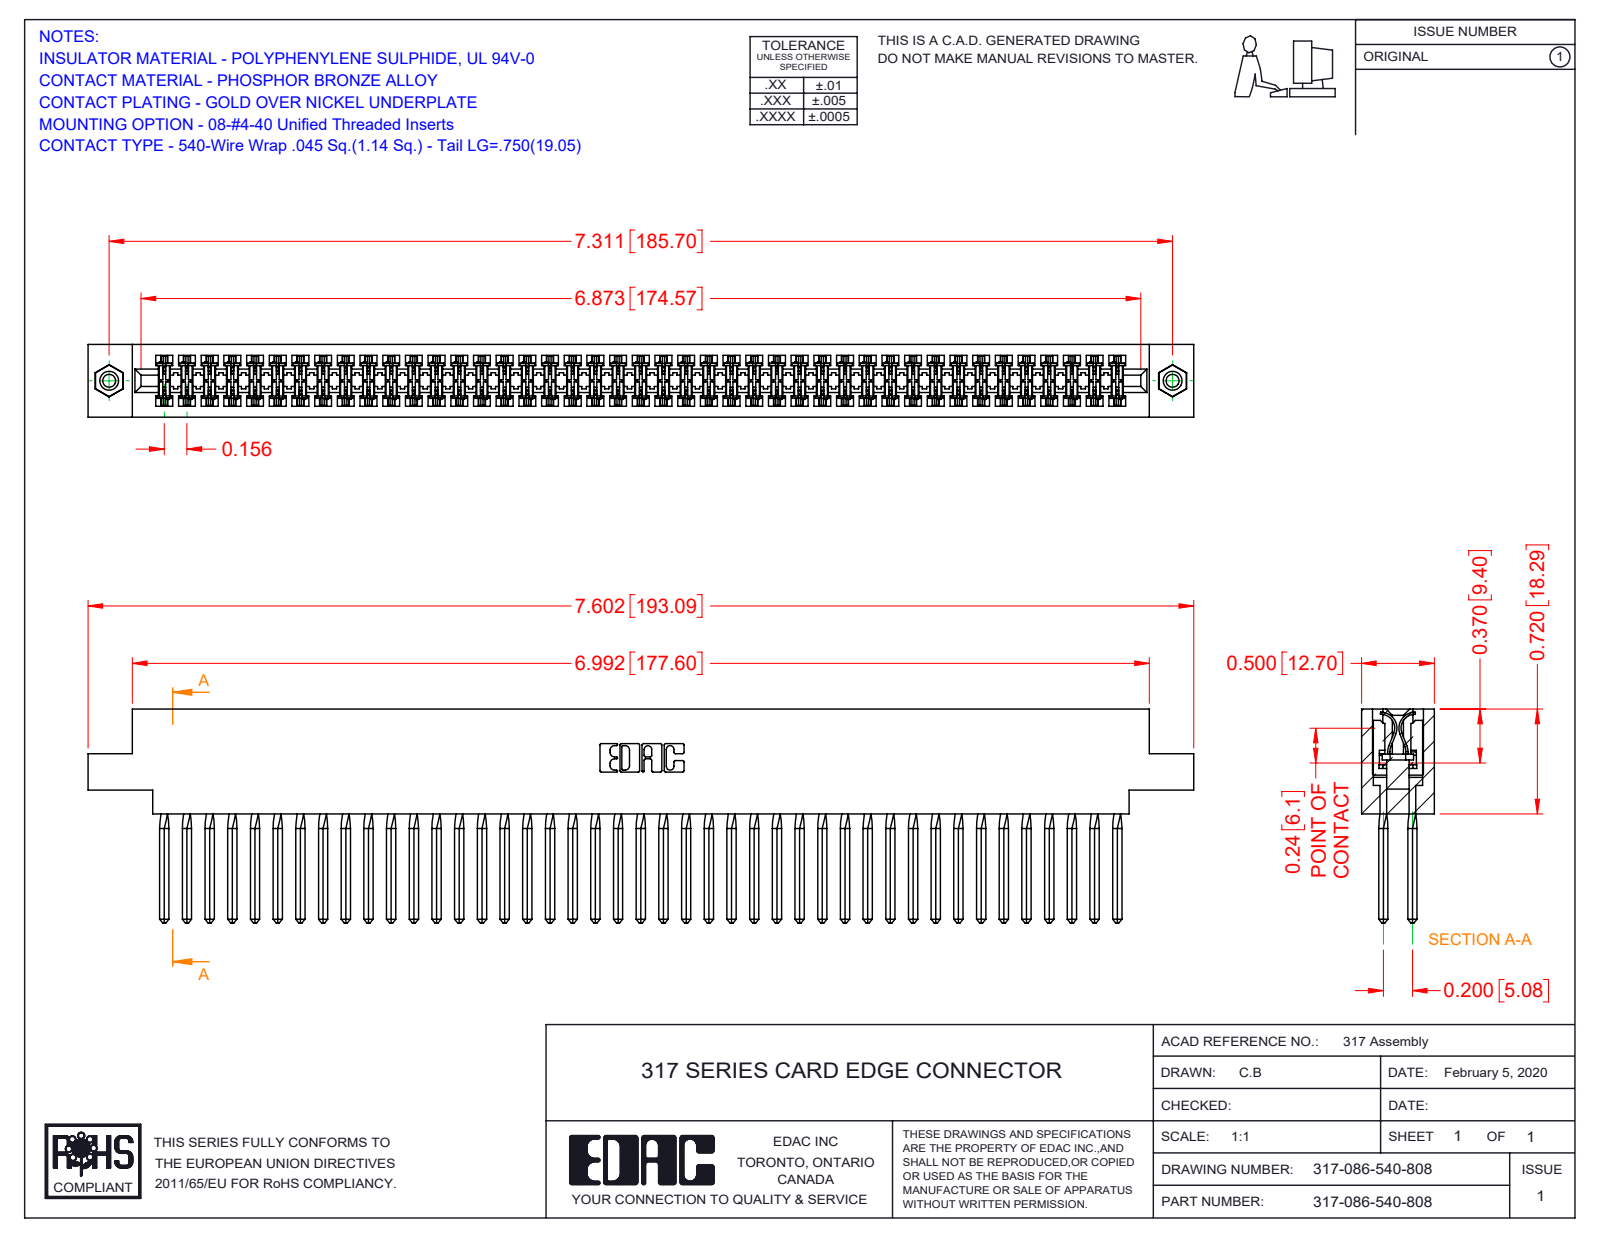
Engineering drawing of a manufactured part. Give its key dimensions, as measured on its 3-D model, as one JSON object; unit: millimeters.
{"part_name": "345-250-001_345-250-003-102; 317-086-540-878; 317-290-001_540; 317 Part_.156 Dia - TI", "step_written_by": "SolidWorks 2016 (CONFIG_CONTROL_DESIGN)", "units": "millimeters", "bodies": {"solids": 89, "faces": 7816, "planar": 6368, "cylindrical": 1088, "other": 360}, "overall_size": [193.1, 37.3, 12.7], "volume_mm3": 32430, "surface_area_mm2": 48420, "round_holes": [[2.3, 2], [3.2, 2], [4, 2]], "round_bosses_or_shafts": [[3.9, 2]], "partial_cylinders_radius": [[0.4, 172], [0.3, 22], [0.2, 6], [0.8, 6], [0.7, 3], [2.4, 2], [2.5, 2], [2.8, 2]], "face_to_face_distances": [12.7, 1.9, 10.8, 8.9, 5, 2.4, 5.1, 2.9, 3.3, 1.2], "hole_center_spacings": [185.7]}
